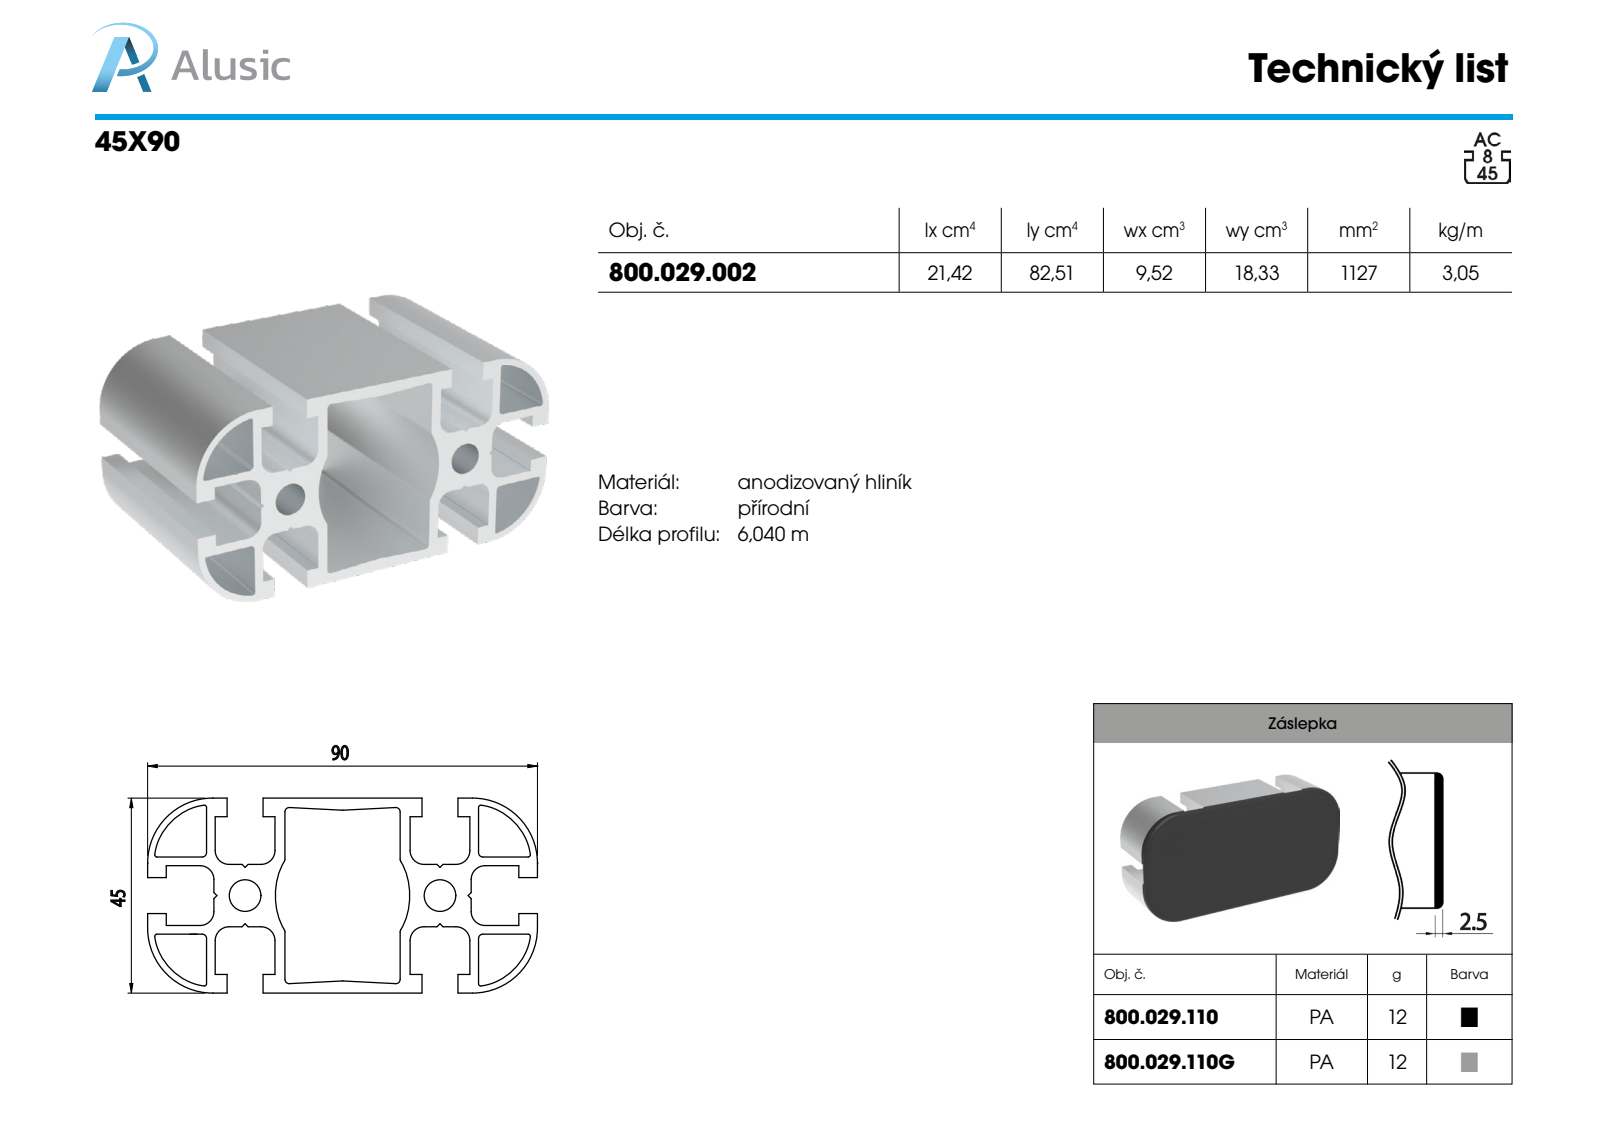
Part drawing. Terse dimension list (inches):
name: 800.029.110
written by: SolidWorks 2011 (CONFIG_CONTROL_DESIGN)
unit: in
bodies: 1 solid, 83 faces (32 planar, 34 cylindrical, 17 other)
size: 3.543 × 1.772 × 0.492
volume: 0.634 in³; area: 16.27 in²
holes: 4× ⌀0.295
bosses: 4× ⌀0.354
rounds: 4× R0.079, 4× R0.591, 2× R0.144
face distances: 0.098, 0.047, 1.772, 0.862, 0.909, 1.819, 1.724, 0.335, 0.236, 0.492
hole spacings: 1.071, 2.843, 3.037
